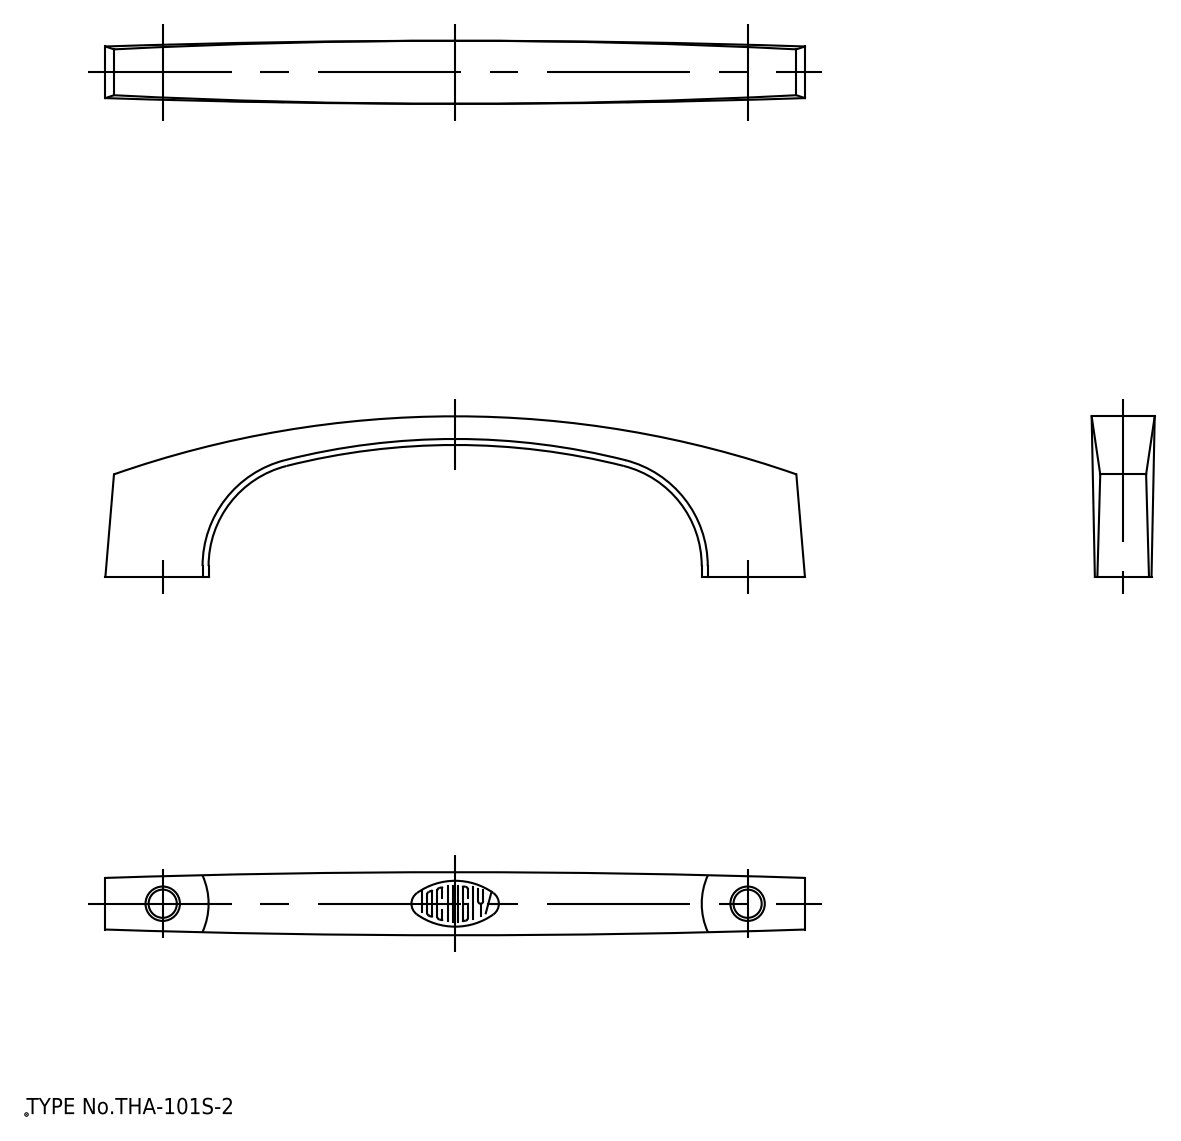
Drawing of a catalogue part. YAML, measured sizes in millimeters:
step_written_by: "spGate 19.8.4 (****-****-****-****) (AUTOMOTIVE_DESIGN)"
units: millimeters
bodies: {solids: 1, faces: 18, planar: 6, cylindrical: 7, other: 5}
overall_size: [122, 28, 11.01]
volume: 11392
surface_area: 5714
round_holes:
  - {diameter: 6, count: 2}
partial_cylinders:
  - {radius: 12, count: 2}
  - {radius: 180, count: 1}
face_to_face_distances: [10]
hole_center_spacings: [102]
